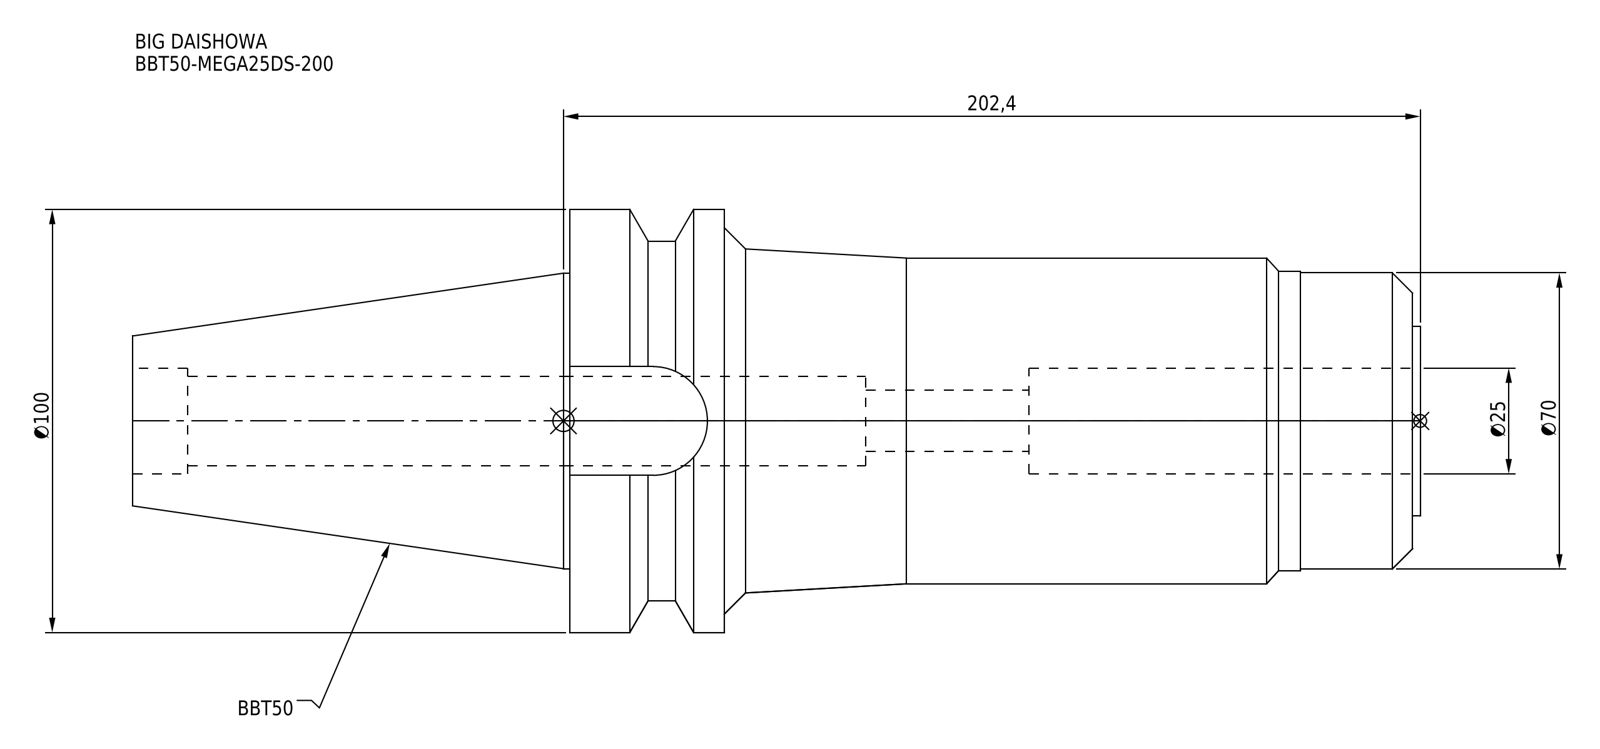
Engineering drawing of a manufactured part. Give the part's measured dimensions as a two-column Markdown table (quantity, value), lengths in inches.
| quantity | value |
| --- | --- |
| part name | BBT50-MEGA25DS-200 |
| STEP written by | CREO PARAMETRIC BY PTC INC, 2016380 (AUTOMOTIVE_DESIGN) |
| units | inches |
| bodies | 1 solid, 57 faces (15 planar, 28 cylindrical, 14 other) |
| overall size | 11.976 × 3.937 × 3.937 |
| volume | 69.08 in³ |
| surface area | 159.1 in² |
| round holes (diameter × count) | 0.571 × 1, 0.835 × 1, 0.984 × 1 |
| round bosses / shafts (diameter × count) | 3.937 × 1, 3.346 × 1, 3.031 × 1, 2.783 × 1, 2.756 × 1, 2.75 × 1, 1.764 × 1 |
| partial cylindrical surfaces (radius × count) | 0.506 × 1 |
| main face-to-face distances | 1.437, 6.402, 7.839, 0.071, 6.472, 7.909, 11.976, 11.906, 5.504, 4.067 |
